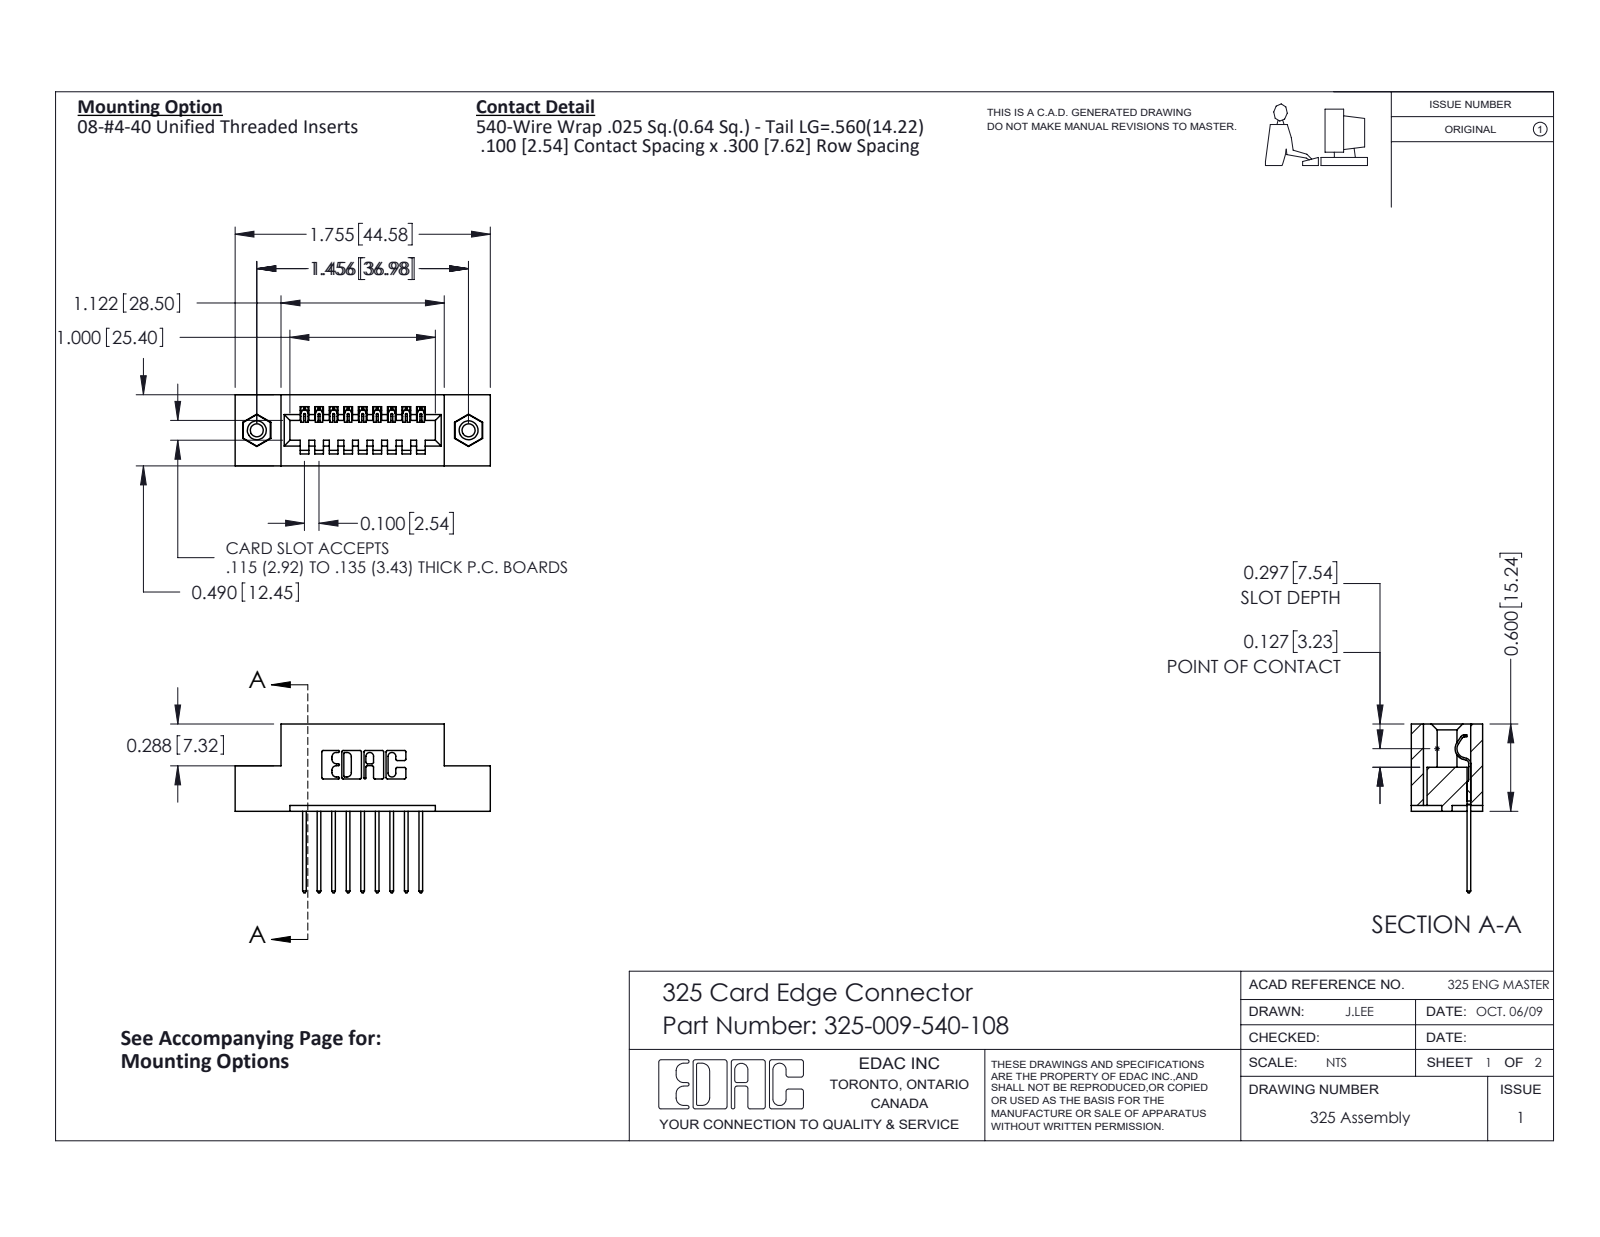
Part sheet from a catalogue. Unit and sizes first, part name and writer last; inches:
Units: inches
Overall size (bounding box): 1.755 × 1.16 × 0.49
Round holes (diameter × count): ⌀0.089 ×2, ⌀0.125 ×2, ⌀0.16 ×2
Round bosses / shafts (diameter × count): ⌀0.155 ×2
Partial cylindrical surfaces — rounded edges, fillets, slot ends (radius × count): R0.01 ×22, R0.006 ×18, R0.01 ×18, R0.007 ×6, R0.031 ×6, R0.026 ×3, R0.014 ×1, R0.022 ×1
Main face-to-face distances: 0.3, 0.04, 0.083, 0.407, 0.1, 0.49, 0.2, 0.6, 0.4, 0.107
Hole centre spacings: 1.456
Volume: 0.33 in³ · Surface area: 8.449 in²
Bodies: 12 solids, 696 faces (480 planar, 200 cylindrical, 16 other)
Part name (STEP PRODUCT): 345-250-001_345-250-003-102; 325-009-540-108; 325-292-001_325-293-140; 325 Part_TI
STEP written by: SolidWorks 2016 (CONFIG_CONTROL_DESIGN)
